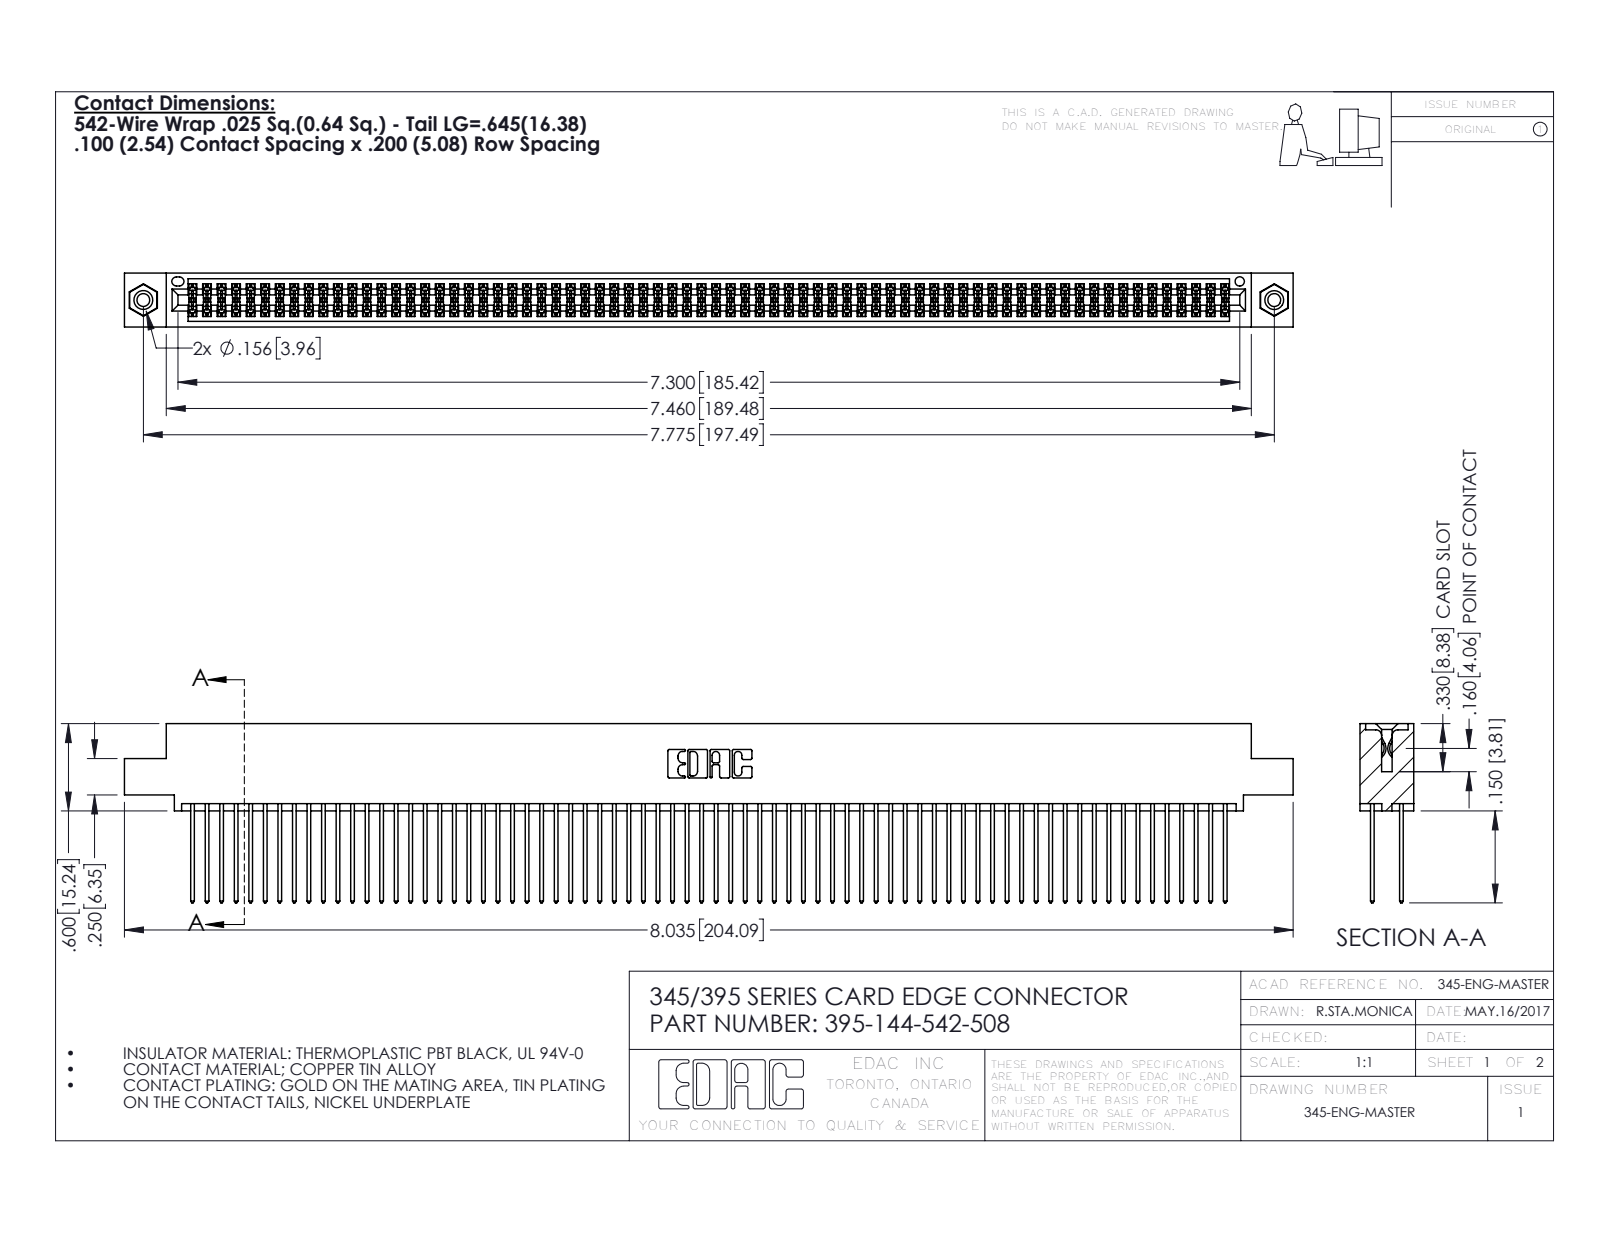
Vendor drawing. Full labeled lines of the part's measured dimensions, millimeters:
Part name (STEP PRODUCT): 345-292-001_345-293-142; 345-250-001_345-250-003-102; 345 Part_0.110 Offset - 0.156 Dia-TI; 395-144-542-508
STEP written by: SolidWorks 2016 (CONFIG_CONTROL_DESIGN)
Units: millimetres
Bodies: 147 solids, 7390 faces (4868 planar, 2506 cylindrical, 16 other)
Overall size (bounding box): 204.1 × 31.3 × 9.4
Volume: 20 700 mm³ · Surface area: 34 410 mm²
Round holes (diameter × count): ⌀2.3 ×2, ⌀3.2 ×2, ⌀4 ×2, ⌀1.6 ×1
Round bosses / shafts (diameter × count): ⌀3.9 ×2
Partial cylindrical surfaces — rounded edges, fillets, slot ends (radius × count): R0.2 ×216, R0.3 ×144, R0.3 ×22, R0.2 ×6, R0.8 ×6, R0.7 ×3, R0.4 ×2, R0.5 ×2
Main face-to-face distances: 1.8, 7.6, 5.1, 2.5, 6.9, 0.6, 5.7, 9.4, 4.4, 3.8
Hole centre spacings: 6.9, 191.5, 197.5
